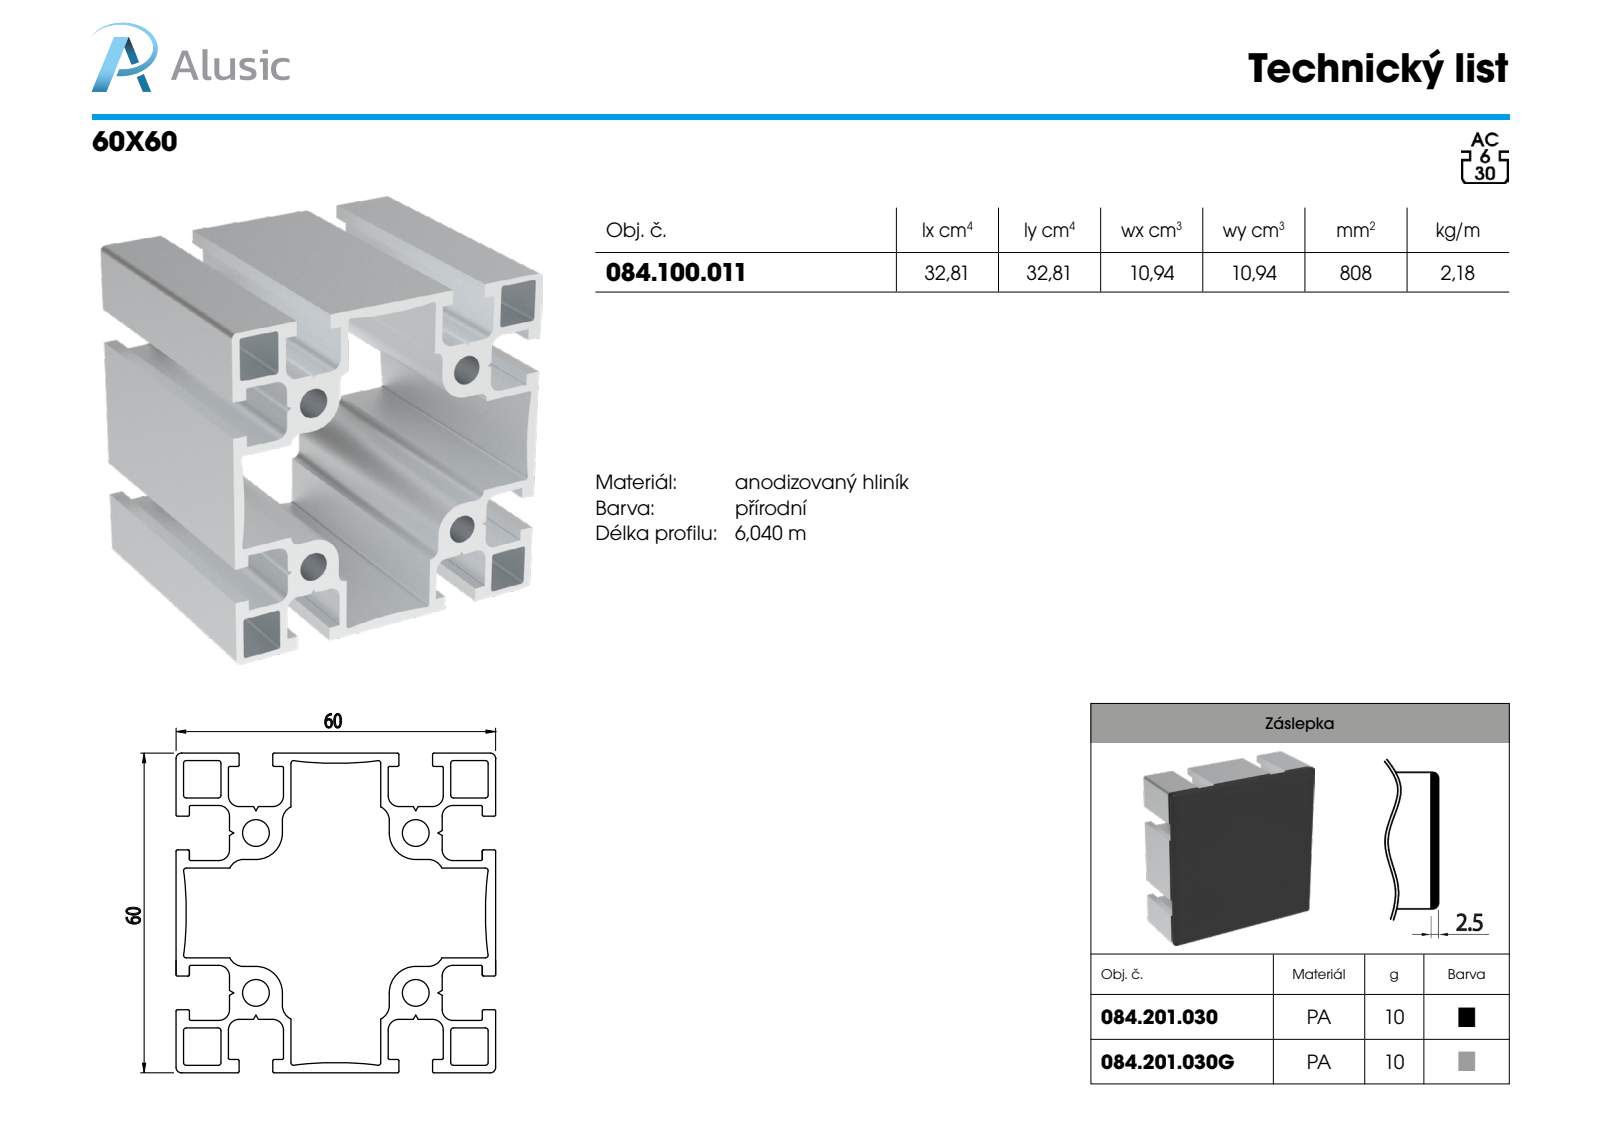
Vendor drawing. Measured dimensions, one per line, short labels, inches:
name: 084.100.011
written by: SolidWorks 2011 (CONFIG_CONTROL_DESIGN)
unit: in
bodies: 1 solid, 205 faces (134 planar, 71 cylindrical, 0 other)
size: 3.937 × 2.362 × 2.362
volume: 4.89 in³; area: 133.7 in²
holes: 4× ⌀0.203
rounds: 24× R0.02, 16× R0.079, 8× R0.059, 4× R0.039, 4× R0.195, 4× R2.467
face distances: 0.055, 1.181, 1.514, 2.362, 0.461, 0.333, 0.848, 0.793, 1.974, 2.03
hole spacings: 1.181, 1.67
